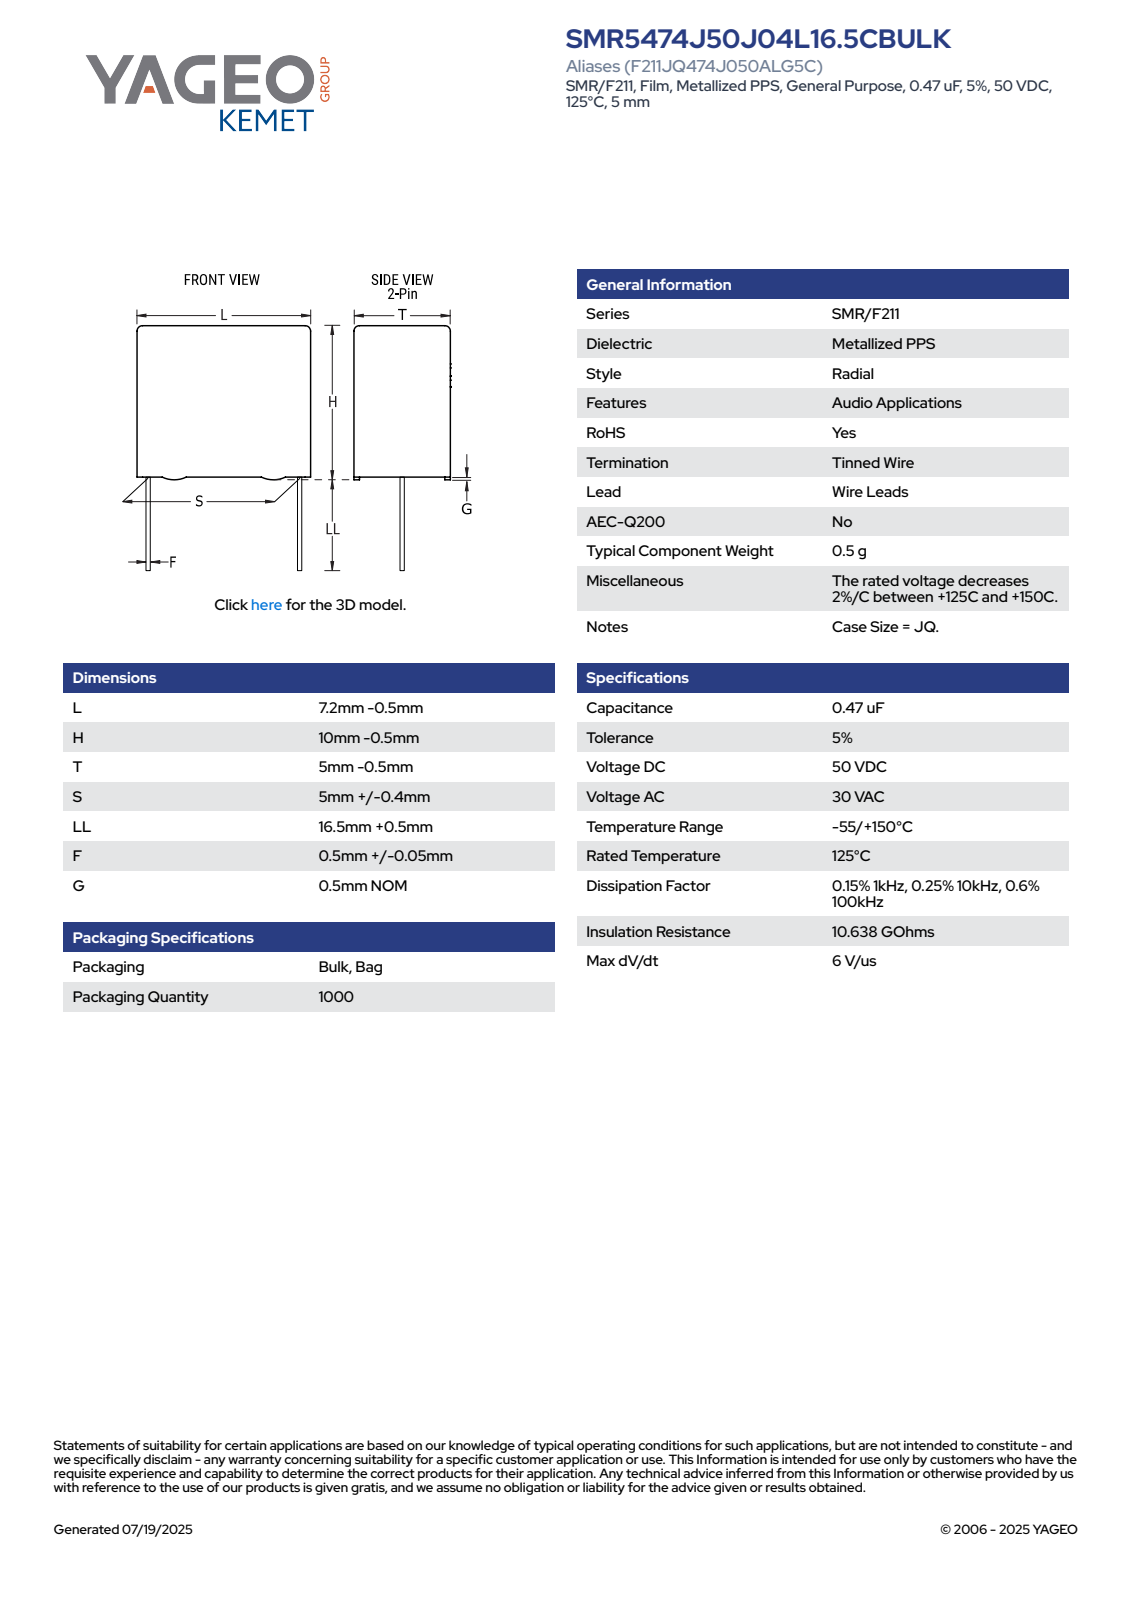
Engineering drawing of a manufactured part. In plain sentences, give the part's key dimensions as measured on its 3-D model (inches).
The part is named "CFR_RBG_7.2X10X5_L6.7H9.5T4.5S5LL17F0.55G0.5". Its 3-D file was written by "SolidWorks 2021 (AUTOMOTIVE_DESIGN)". It is 4 solids with 89 faces: 81 planar, 8 cylindrical and 0 other. Overall it measures 1.043 by 0.264 by 0.177 inches. Its volume is 0.017 cubic inches and its surface area 0.508 square inches. Round bosses or shafts: 2 of diameter 0.022. Partial cylindrical surfaces (rounded edges, fillets, slot ends): 4 of radius 0.02. The main face-to-face distances are 0.177, 0.264, 0.354, 0.167, 0.157, 0.02, 0.374, 0.098, 0.669, 0.689.
